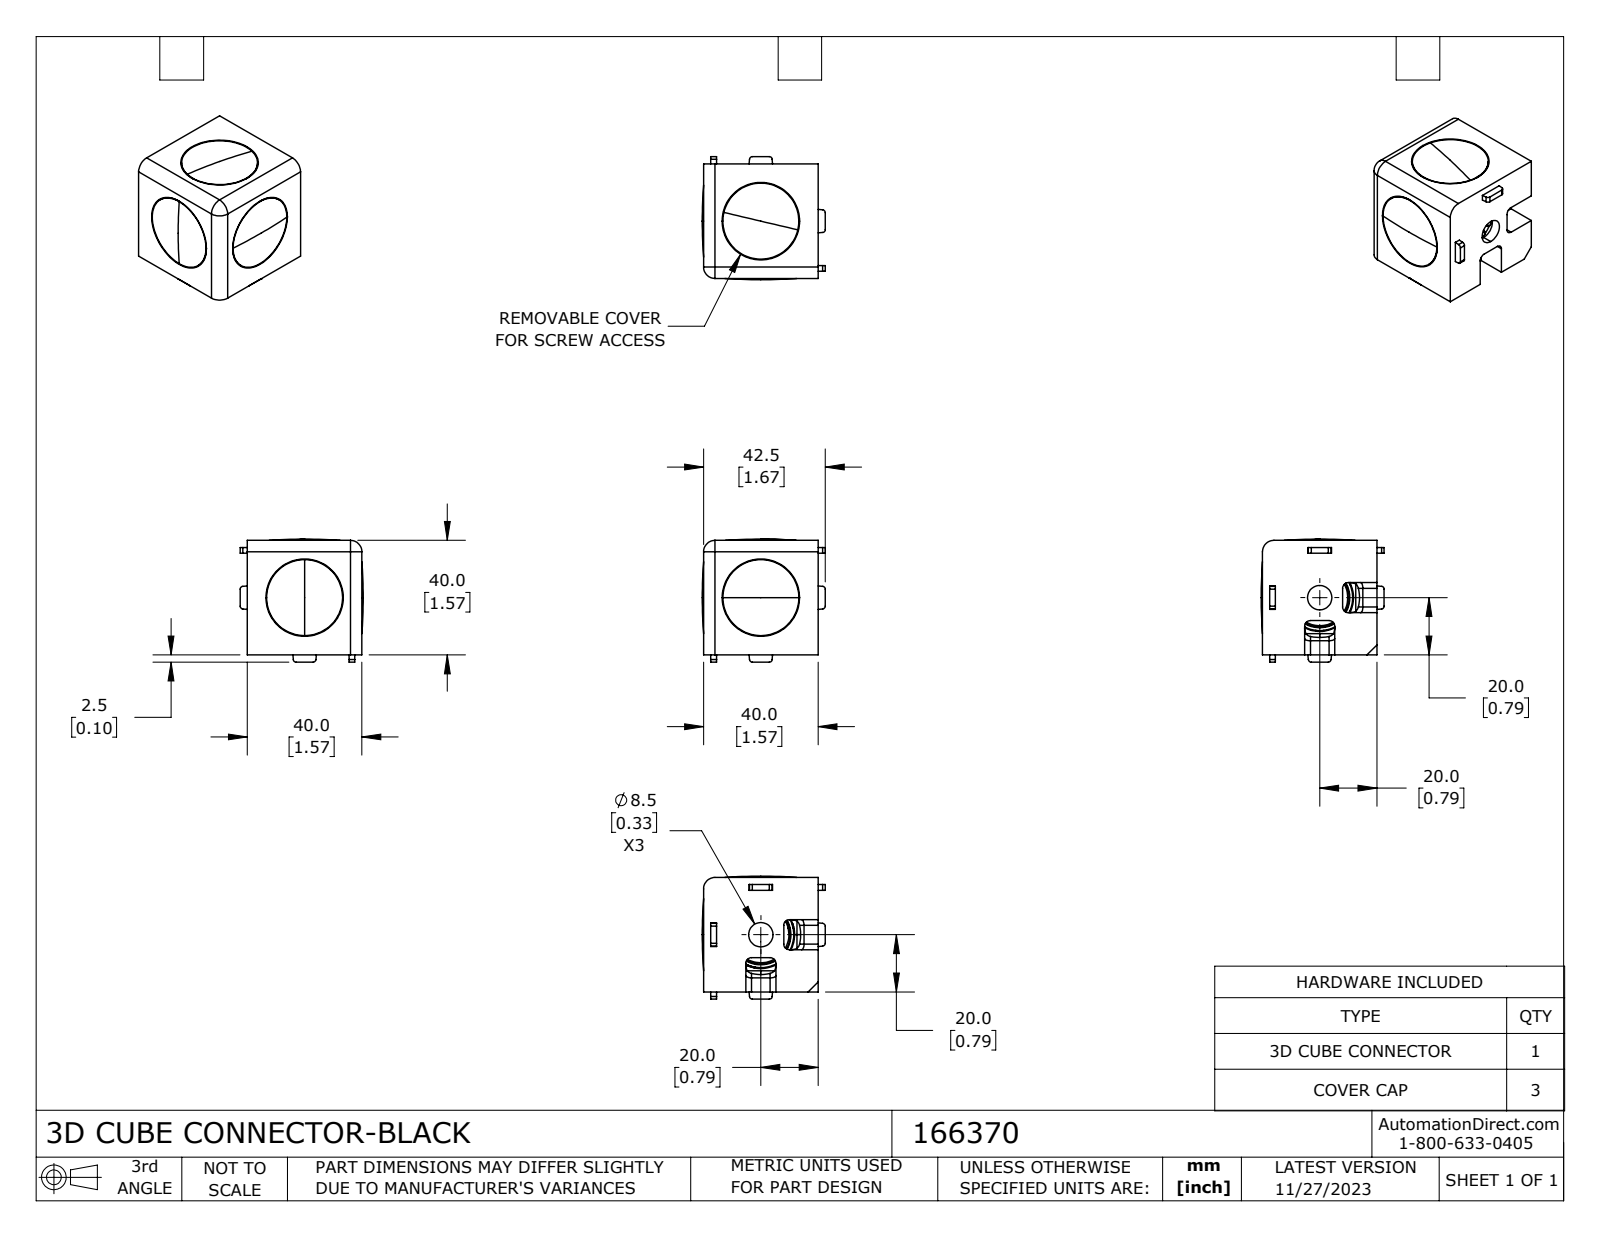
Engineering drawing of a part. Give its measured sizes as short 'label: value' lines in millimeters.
name: 166370
written by: SolidWorks 2023 (CONFIG_CONTROL_DESIGN)
unit: mm
bodies: 4 solids, 259 faces (61 planar, 69 cylindrical, 129 other)
size: 42.95 × 42.95 × 42.93
volume: 37 791 mm³; area: 18 066 mm²
holes: 3× ⌀8.5
bosses: 3× ⌀26.5, 3× ⌀23
rounds: 24× R2, 12× R1, 3× R4
face distances: 40, 14.75, 25.25, 38.95, 1.05, 10.5, 38.93, 1.07, 24.2, 13.7
